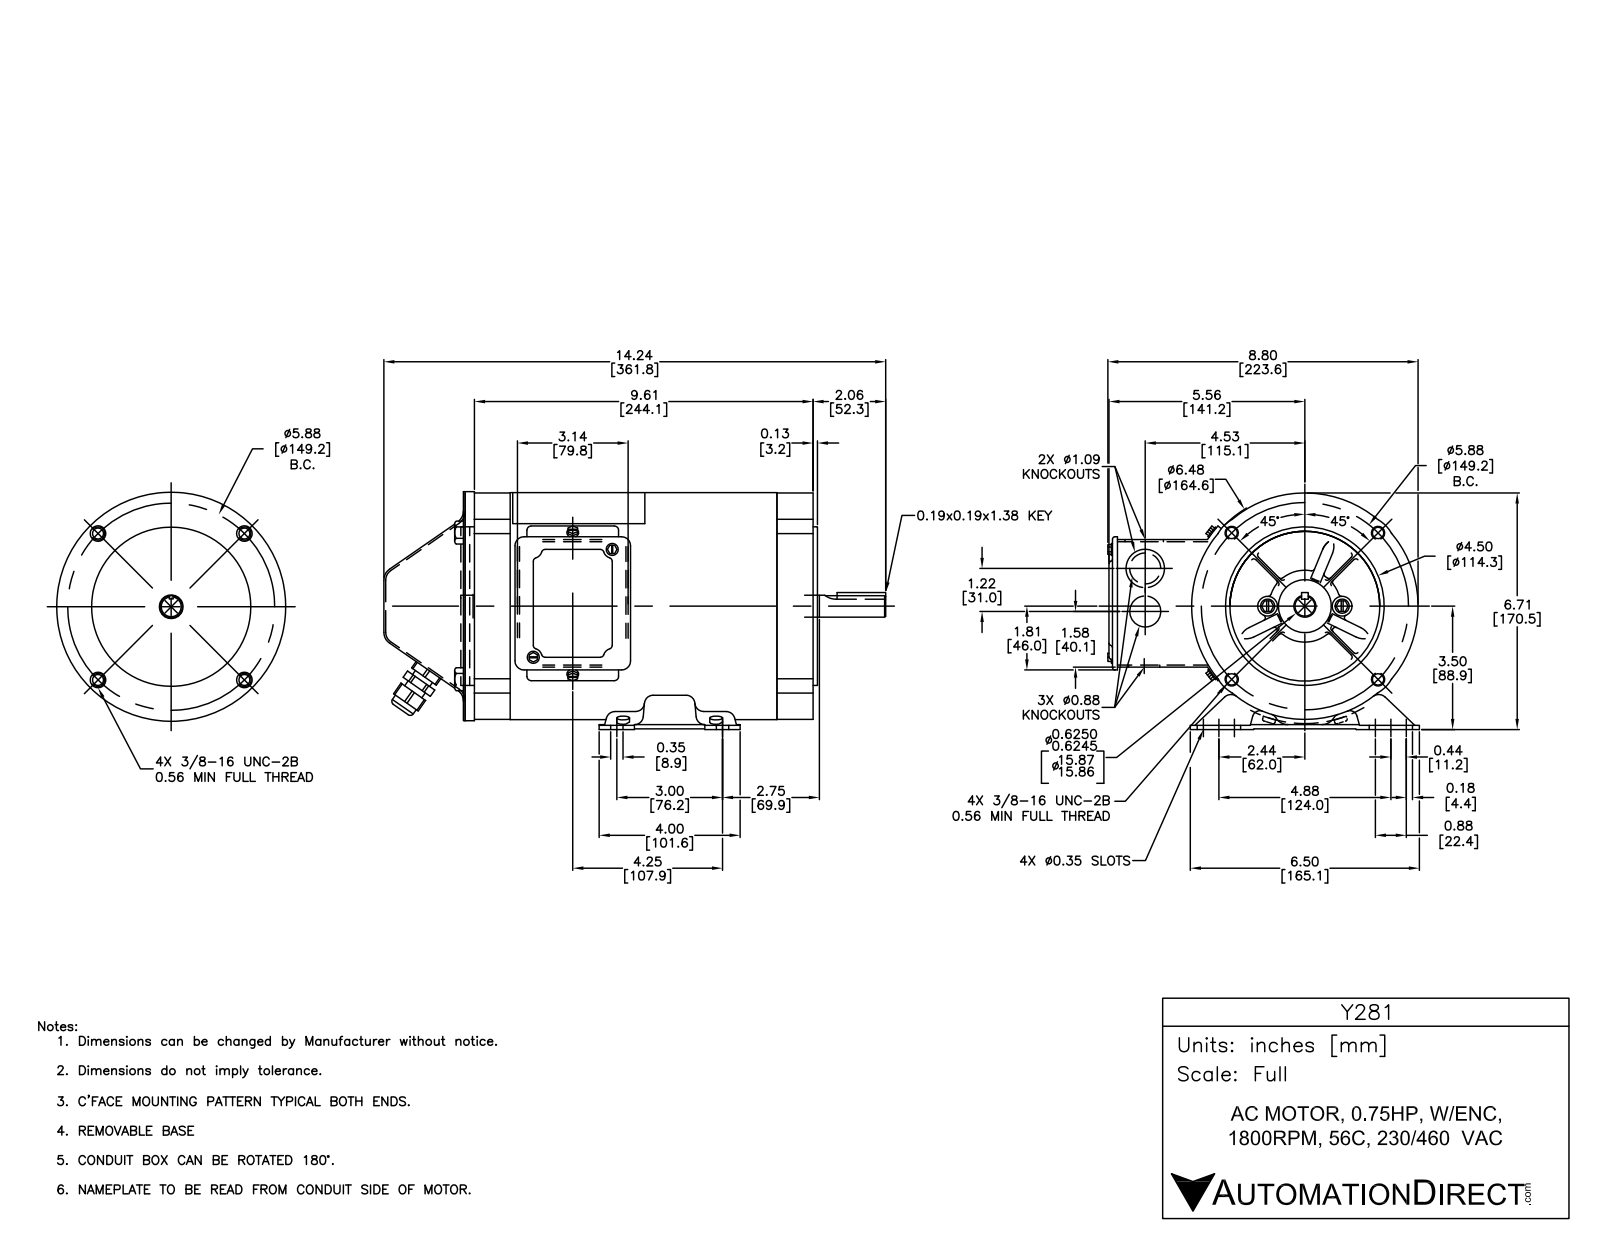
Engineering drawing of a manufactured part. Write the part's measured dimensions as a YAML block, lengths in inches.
part_name: "107388-756_Rev00 r1"
step_written_by: "SolidWorks 2017 (AUTOMOTIVE_DESIGN)"
units: inches
bodies: {solids: 40, faces: 3557, planar: 1326, cylindrical: 828, other: 1403}
overall_size: [13.973, 8.657, 6.723]
volume: 49.31
surface_area: 951.6
round_holes:
  - {diameter: 0.25, count: 12}
  - {diameter: 0.218, count: 8}
  - {diameter: 0.313, count: 6}
  - {diameter: 0.159, count: 4}
  - {diameter: 0.274, count: 4}
  - {diameter: 0.28, count: 4}
  - {diameter: 0.406, count: 4}
  - {diameter: 0.88, count: 3}
  - {diameter: 0.063, count: 2}
  - {diameter: 0.147, count: 2}
  - {diameter: 0.187, count: 2}
  - {diameter: 0.205, count: 2}
round_bosses_or_shafts:
  - {diameter: 0.399, count: 10}
  - {diameter: 0.19, count: 10}
  - {diameter: 0.5, count: 4}
  - {diameter: 0.375, count: 4}
  - {diameter: 0.166, count: 4}
  - {diameter: 0.164, count: 4}
  - {diameter: 0.335, count: 3}
  - {diameter: 6.5, count: 1}
partial_cylinders:
  - {radius: 0.05, count: 46}
  - {radius: 0.06, count: 19}
  - {radius: 0.12, count: 16}
  - {radius: 0.25, count: 16}
  - {radius: 0.13, count: 12}
  - {radius: 0.02, count: 10}
  - {radius: 0.08, count: 10}
  - {radius: 0.175, count: 8}
face_to_face_distances: [0.06, 0.22, 9.39, 9.61, 0.048, 9.658, 3.56, 0.1, 0.041, 0.06]
hole_center_spacings: [2.193, 2.287, 2.451, 2.772, 3.091, 3.774, 3.923, 5.207]
